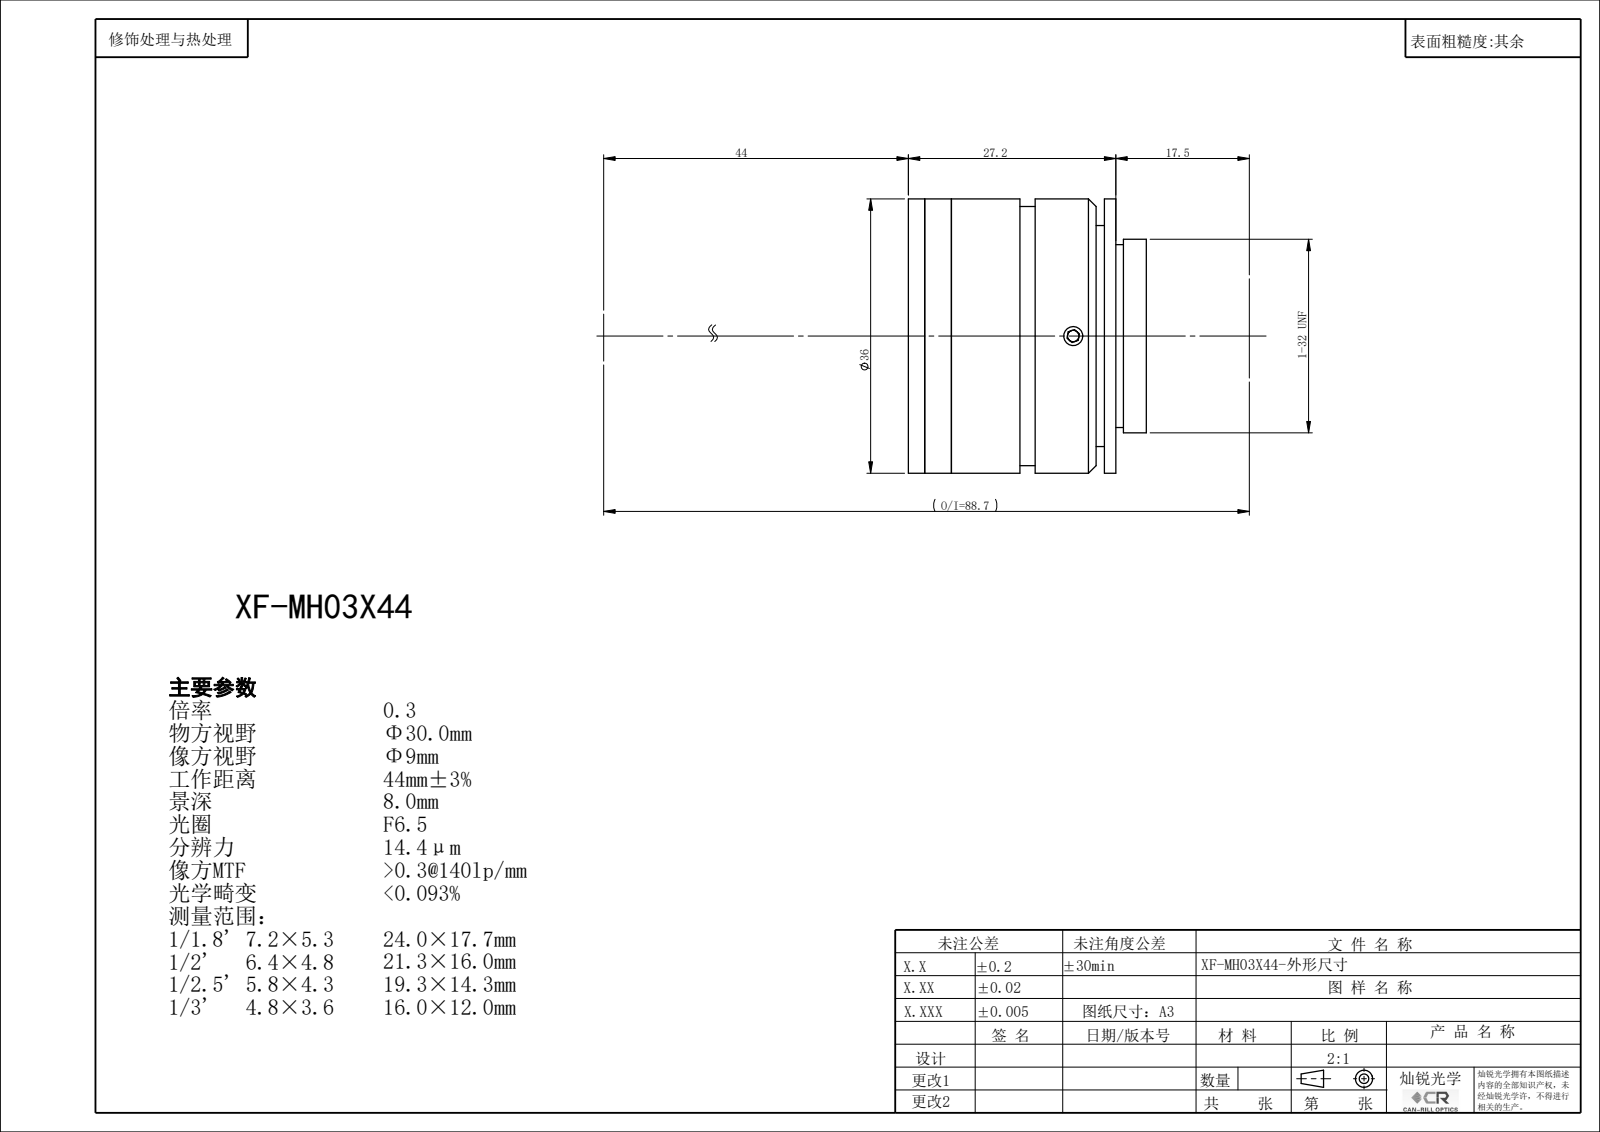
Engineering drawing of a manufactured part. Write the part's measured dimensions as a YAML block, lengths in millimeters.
part_name: "XF-MH03X44"
step_written_by: "SolidWorks 2022 (CONFIG_CONTROL_DESIGN)"
units: millimeters
bodies: {solids: 0, faces: 110, planar: 52, cylindrical: 48, other: 10}
overall_size: [36, 36, 31.24]
round_holes:
  - {diameter: 2.5, count: 3}
  - {diameter: 7, count: 1}
  - {diameter: 8.4, count: 1}
  - {diameter: 10, count: 1}
  - {diameter: 12, count: 1}
  - {diameter: 14, count: 1}
  - {diameter: 16, count: 1}
  - {diameter: 18, count: 1}
  - {diameter: 20, count: 1}
  - {diameter: 21.5, count: 1}
  - {diameter: 22, count: 1}
  - {diameter: 24, count: 1}
round_bosses_or_shafts:
  - {diameter: 36, count: 1}
  - {diameter: 34, count: 1}
  - {diameter: 25.4, count: 1}
face_to_face_distances: [3.5, 5.65, 25.09, 21.59, 2.15, 27.24, 4, 2, 1, 1.5]
